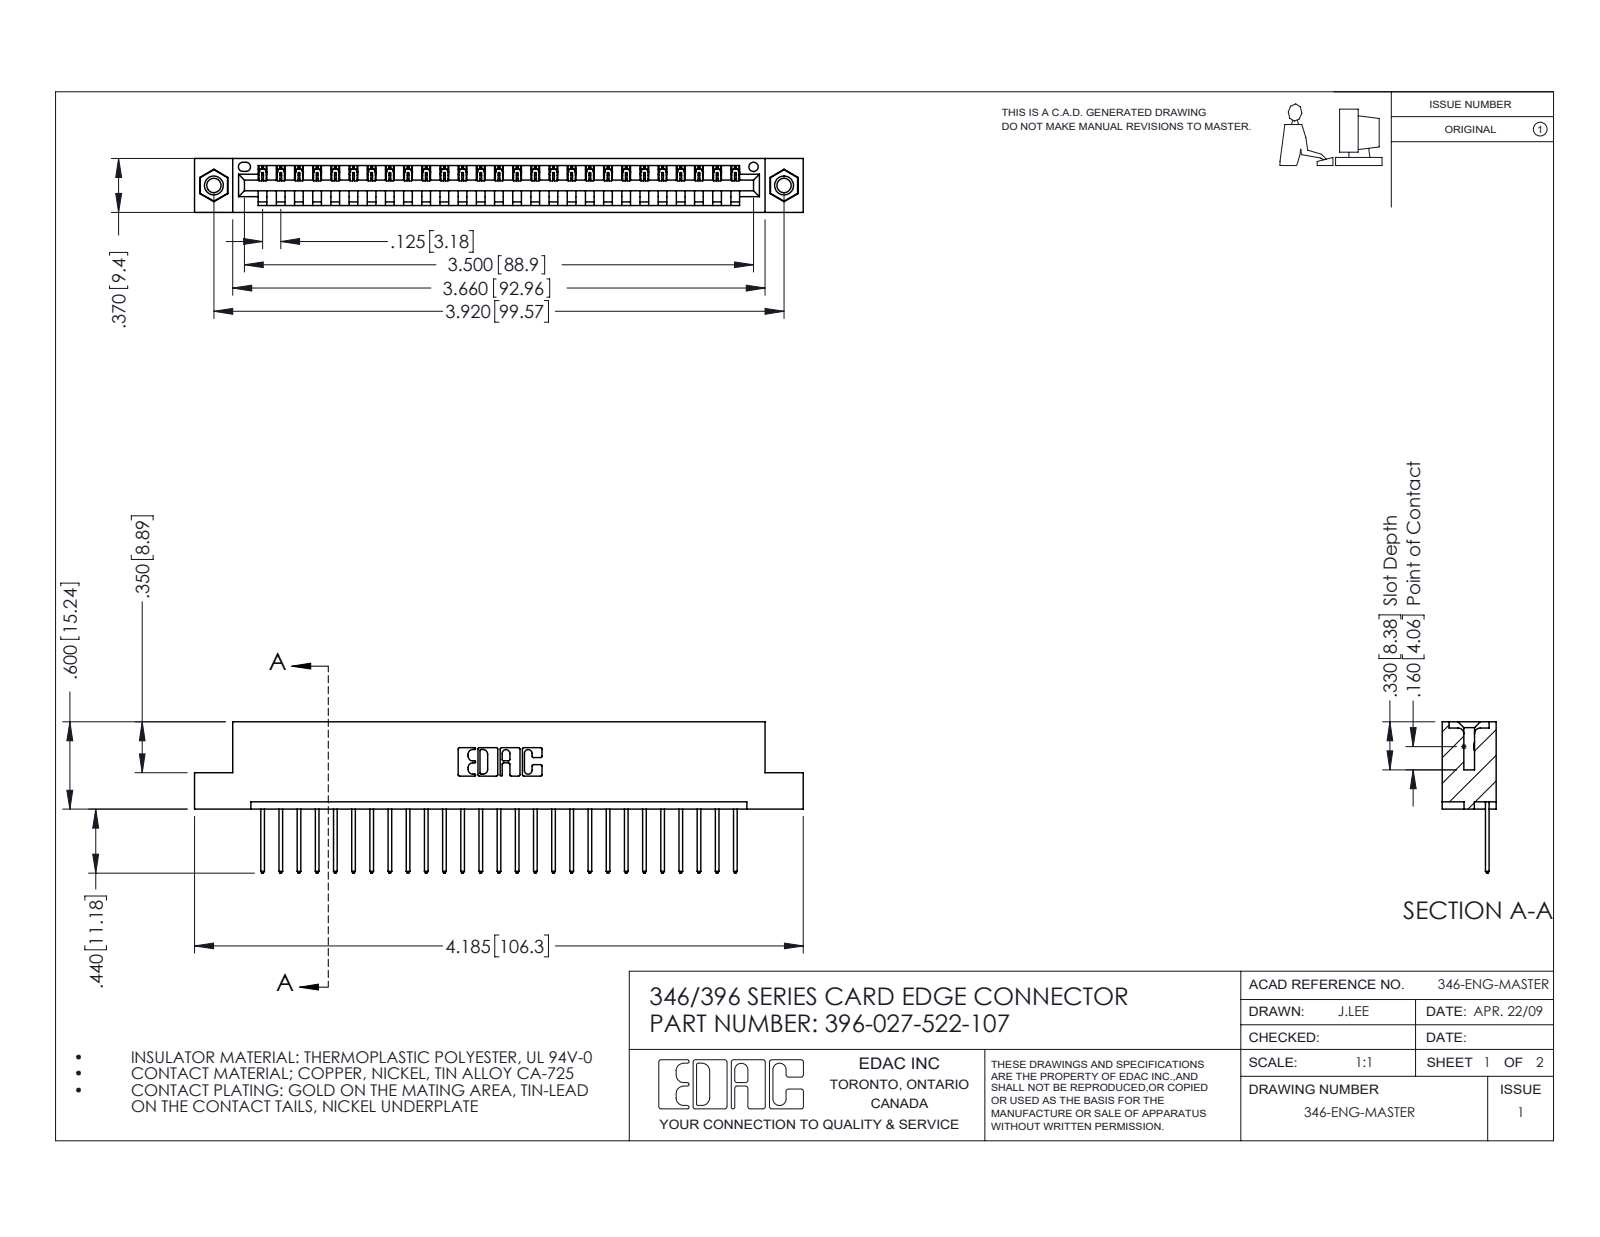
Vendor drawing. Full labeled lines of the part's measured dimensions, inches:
Part name (STEP PRODUCT): 345-292-001_345-293-122; 396-027-522-107; 346 Part_Flush Mounting Lugs - 0.156 Dia-TI; 345-250-001_345-250-005-103
STEP written by: SolidWorks 2016 (CONFIG_CONTROL_DESIGN)
Units: inches
Bodies: 30 solids, 1748 faces (1188 planar, 544 cylindrical, 16 other)
Overall size (bounding box): 4.185 × 1.04 × 0.37
Volume: 0.614 in³ · Surface area: 19.45 in²
Round holes (diameter × count): ⌀0.098 ×2, ⌀0.125 ×2, ⌀0.156 ×2, ⌀0.064 ×1
Round bosses / shafts (diameter × count): ⌀0.155 ×2
Partial cylindrical surfaces — rounded edges, fillets, slot ends (radius × count): R0.006 ×54, R0.01 ×54, R0.01 ×22, R0.007 ×6, R0.031 ×6, R0.026 ×3, R0.031 ×2, R0.04 ×2
Main face-to-face distances: 0.048, 0.322, 0.37, 0.25, 0.072, 0.298, 0.025, 0.148, 0.222, 0.1
Hole centre spacings: 0.246, 3.712, 3.92
